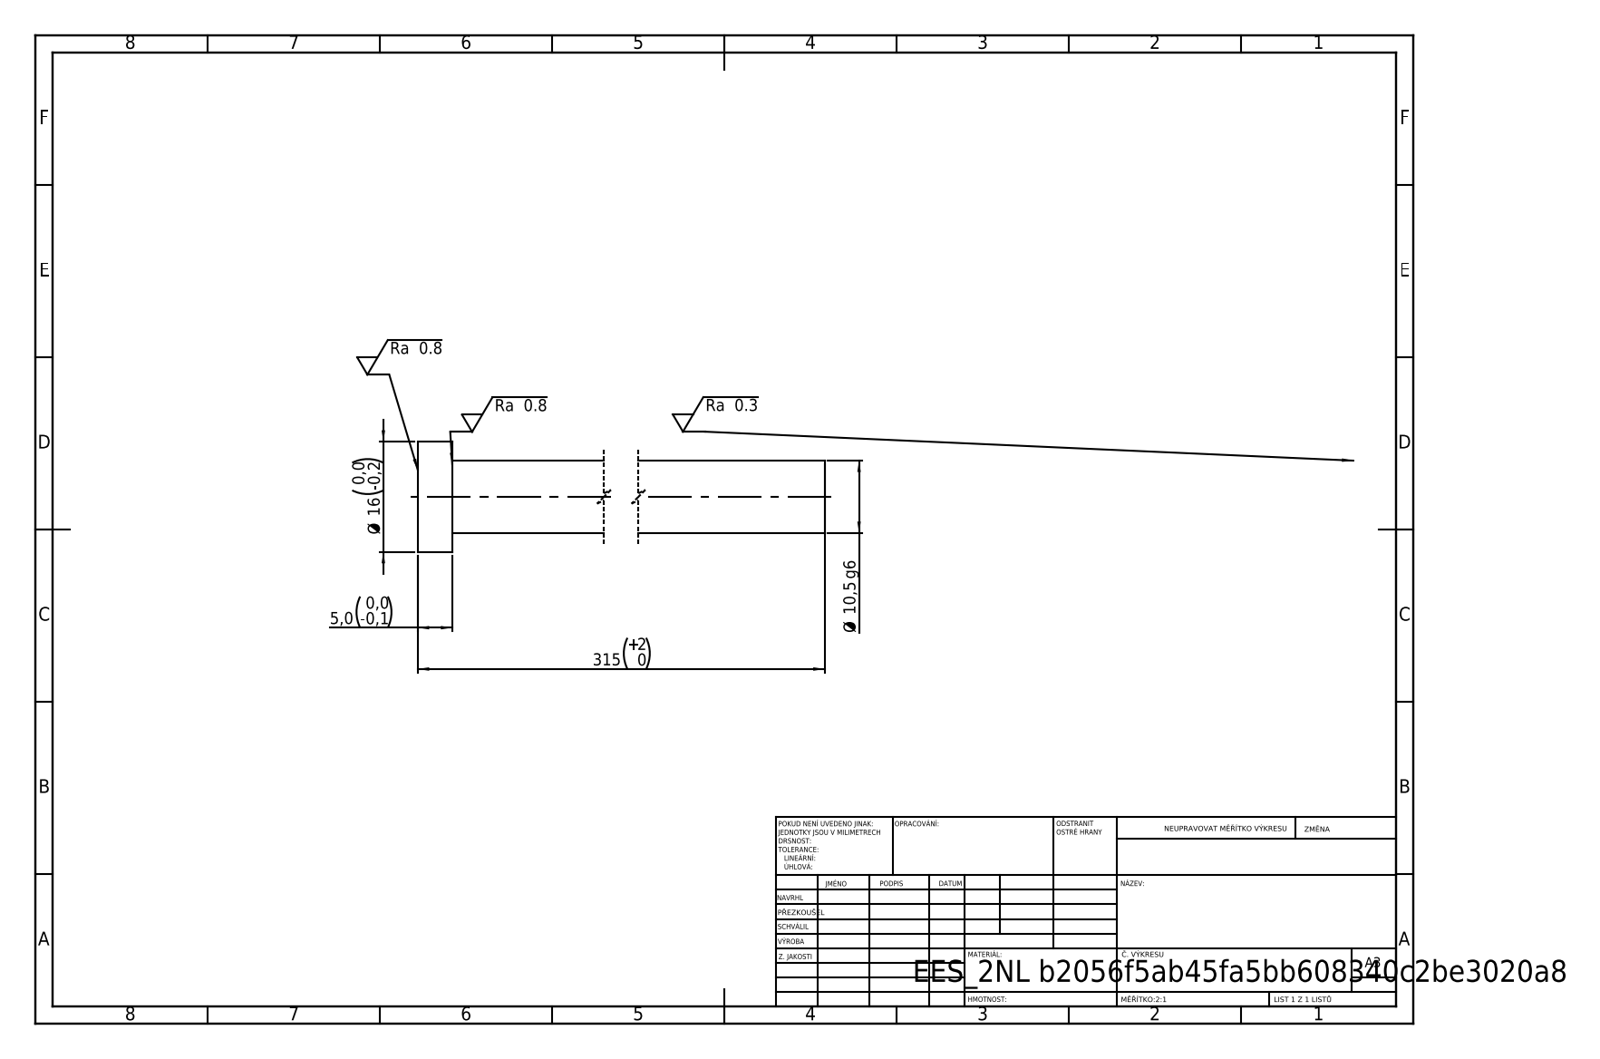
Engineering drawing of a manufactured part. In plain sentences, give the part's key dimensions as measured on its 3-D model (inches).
Its 3-D file was written by "SolidWorks 2019 (CONFIG_CONTROL_DESIGN)". It is 1 solid with 7 faces: 3 planar, 4 cylindrical and 0 other. Overall it measures 12.402 by 0.63 by 0.63 inches. Its volume is 1.699 cubic inches and its surface area 16.86 square inches. Round bosses or shafts: 1 of diameter 0.63, 1 of diameter 0.413. The main face-to-face distances are 0.197, 12.402, 12.205.
